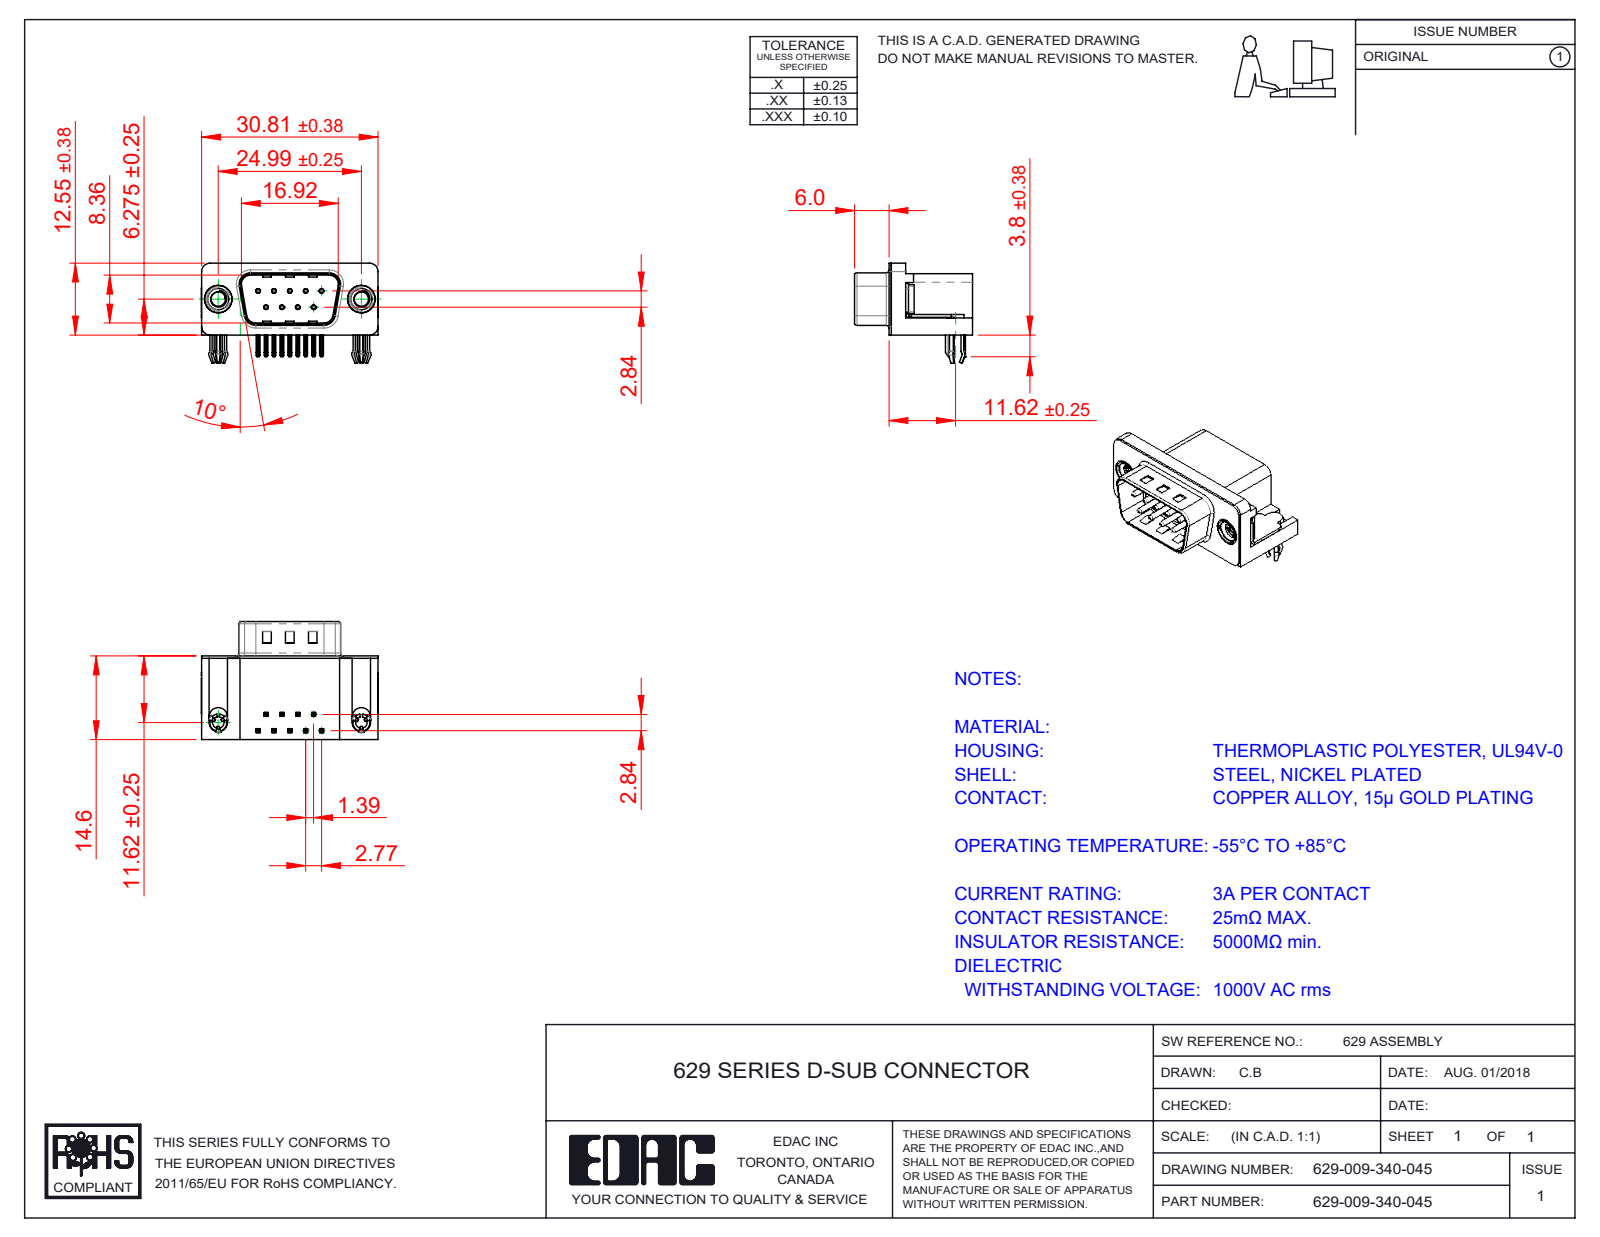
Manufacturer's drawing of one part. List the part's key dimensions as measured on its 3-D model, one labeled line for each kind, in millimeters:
Part name (STEP PRODUCT): 629 3 Prong Board Lock; 629 Housing_09 Socket; 629-009-340-045; 629 Contact Top (+3 more)
STEP written by: SolidWorks 2020 (CONFIG_CONTROL_DESIGN)
Units: millimetres
Bodies: 15 solids, 1093 faces (609 planar, 325 cylindrical, 159 other)
Overall size (bounding box): 30.89 × 20.6 × 17.48
Volume: 3 725 mm³ · Surface area: 4 822 mm²
Round holes (diameter × count): ⌀0.35 ×9, ⌀0.8 ×9, ⌀2 ×2, ⌀2.5 ×2, ⌀4 ×2, ⌀4.8 ×2, ⌀5 ×2
Round bosses / shafts (diameter × count): ⌀0.75 ×9, ⌀4.9 ×2, ⌀4.75 ×2, ⌀3.9 ×2, ⌀3 ×2
Partial cylindrical surfaces — rounded edges, fillets, slot ends (radius × count): R0.25 ×48, R0.12 ×18, R1 ×16, R0.5 ×9, R1.5 ×8, R1.6 ×8, R0.9 ×4, R2 ×4
Main face-to-face distances: 0.4, 14.2, 10.35, 14.6, 0.5, 2.9, 11.7, 2.5, 2.1, 6.7
Hole centre spacings: 3.16, 2.77, 5.54, 5.03, 5.04, 8.31, 7.48, 7.49
